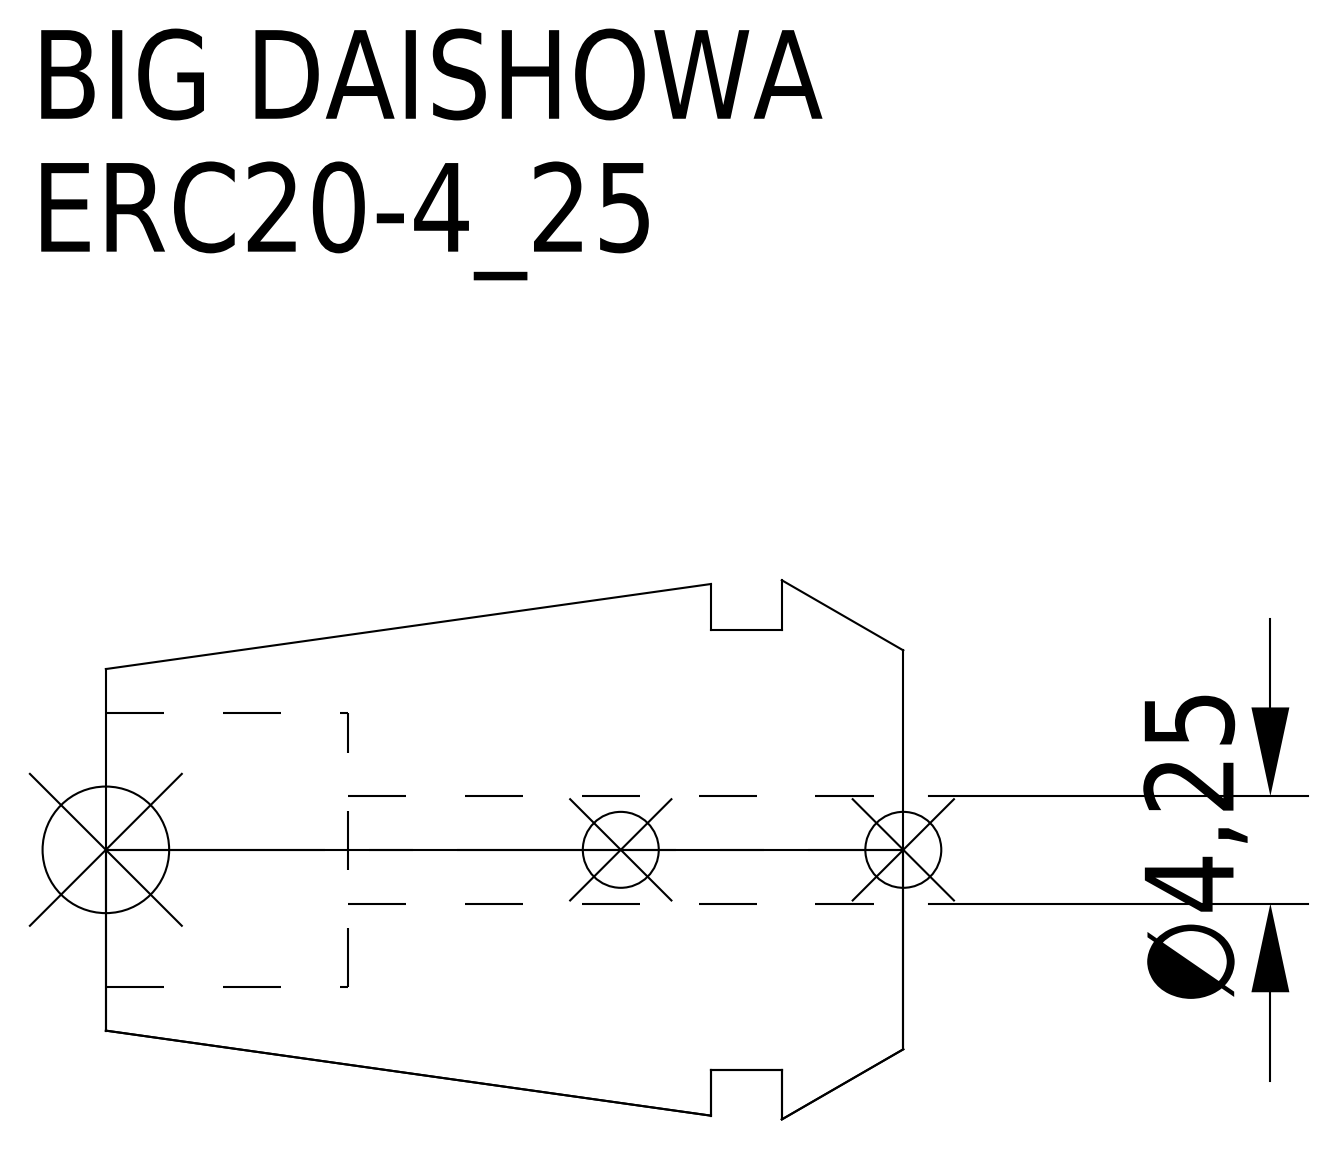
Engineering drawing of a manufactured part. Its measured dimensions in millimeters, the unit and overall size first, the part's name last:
Units: millimetres
Overall size (bounding box): 31.5 × 21.3 × 21.3
Round holes (diameter × count): ⌀4.25 ×1, ⌀10.8 ×1
Round bosses / shafts (diameter × count): ⌀17.4 ×1
Main face-to-face distances: 4.8, 7.6, 2.8, 21.95, 17.15, 14.35, 31.5, 26.7, 23.9, 9.55
Volume: 6 696 mm³ · Surface area: 2 984 mm²
Bodies: 1 solid, 15 faces (5 planar, 6 cylindrical, 4 other)
Part name (STEP PRODUCT): ERC20-4_25
STEP written by: CREO PARAMETRIC BY PTC INC, 2016380 (AUTOMOTIVE_DESIGN)
